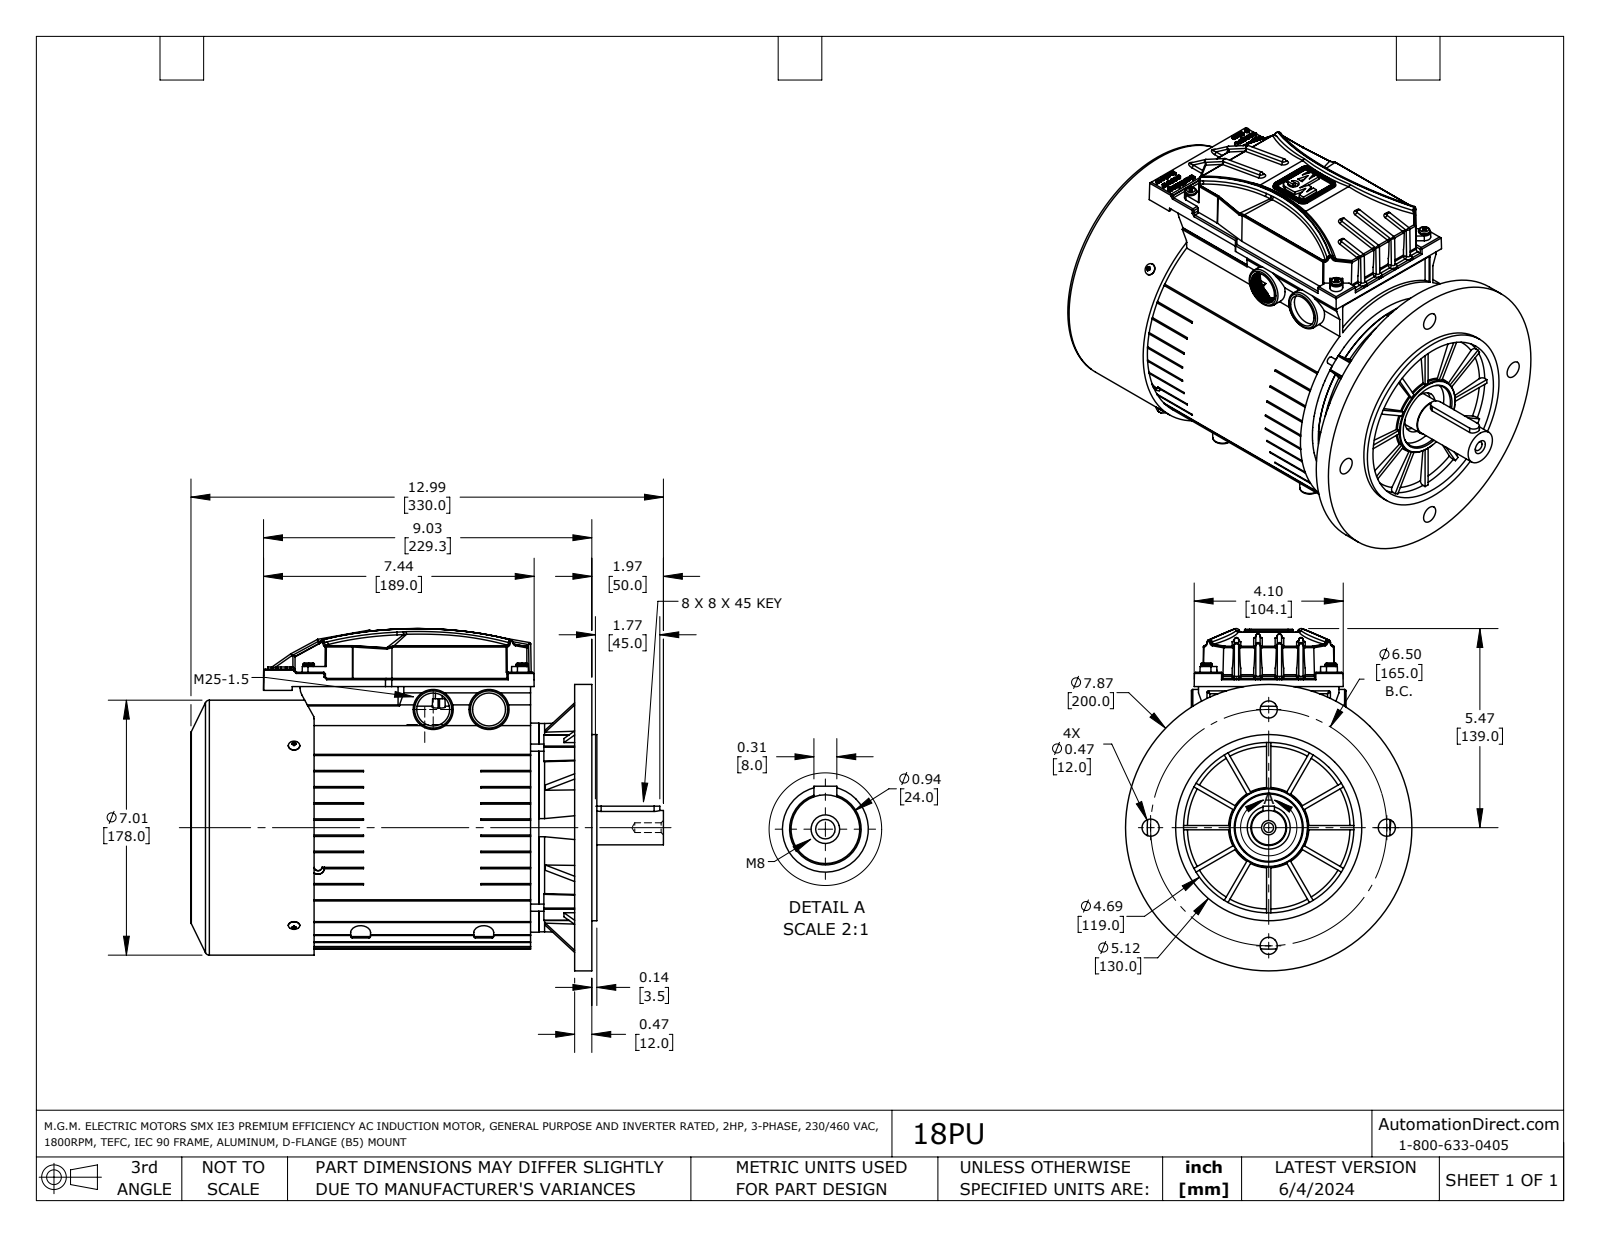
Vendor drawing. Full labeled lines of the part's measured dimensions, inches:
Part name (STEP PRODUCT): 18PU
STEP written by: SolidWorks 2021 (AUTOMOTIVE_DESIGN)
Units: inches
Bodies: 13 solids, 3585 faces (1529 planar, 1052 cylindrical, 1004 other)
Overall size (bounding box): 12.992 × 9.41 × 7.874
Volume: 356 in³ · Surface area: 755 in²
Round holes (diameter × count): ⌀0.13 ×5, ⌀0.315 ×5, ⌀0.165 ×4, ⌀0.177 ×4, ⌀0.472 ×4, ⌀0.098 ×3, ⌀0.906 ×2, ⌀0.268 ×1, ⌀1.043 ×1, ⌀1.122 ×1, ⌀1.181 ×1, ⌀1.732 ×1
Round bosses / shafts (diameter × count): ⌀0.315 ×8, ⌀0.197 ×6, ⌀0.138 ×6, ⌀0.079 ×4, ⌀0.276 ×3, ⌀1.102 ×2, ⌀7.874 ×1, ⌀7.008 ×1
Partial cylindrical surfaces — rounded edges, fillets, slot ends (radius × count): R0.039 ×440, R0.016 ×48, R0.059 ×47, R0.008 ×32, R0.004 ×24, R0.031 ×22, R0.02 ×16, R0.033 ×16
Main face-to-face distances: 1.457, 0.197, 10.925, 9.469, 0.02, 1.26, 10.728, 0.118, 0.157, 1.685
Hole centre spacings: 2.437, 5.874, 3.11, 3.248, 3.386, 4.398, 4.593, 1.051
